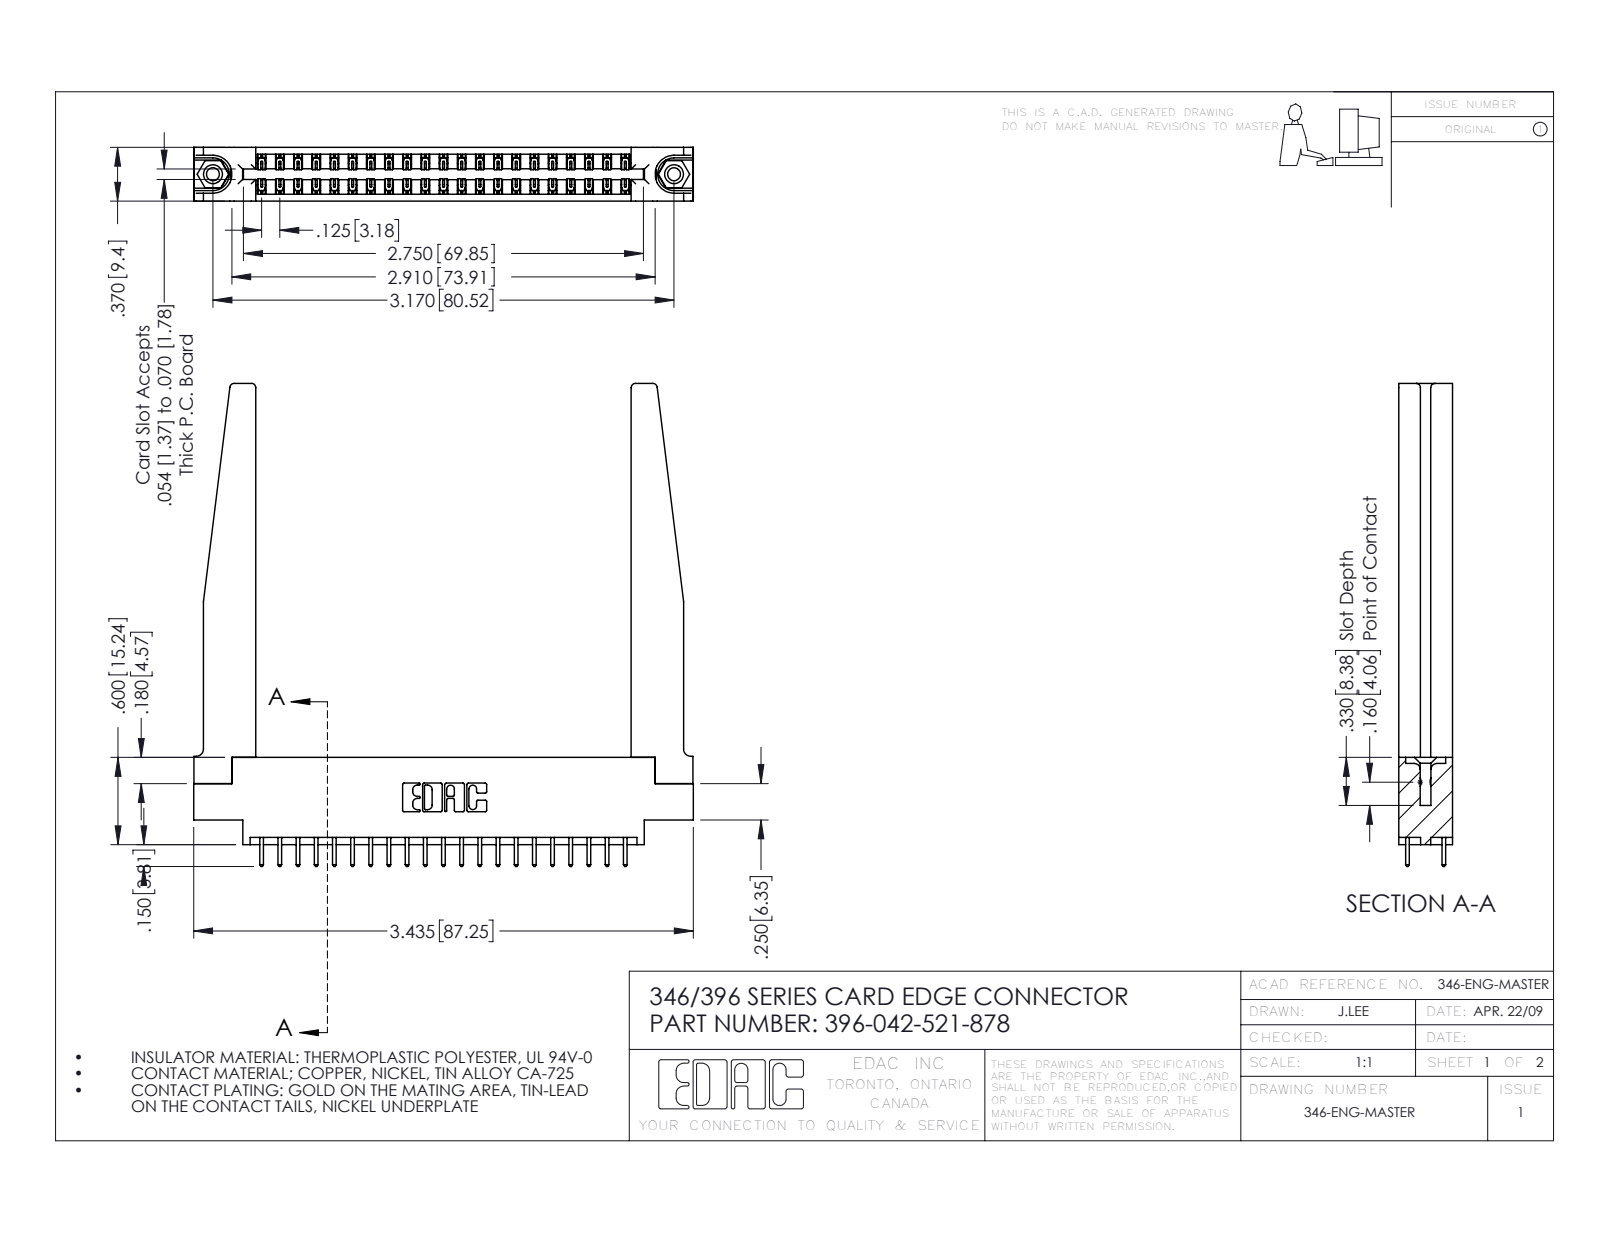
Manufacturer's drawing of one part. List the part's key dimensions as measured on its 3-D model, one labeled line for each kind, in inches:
Part name (STEP PRODUCT): 345-250-001_345-250-001-102; 346 Part_0.170 Offset - 0.156 Dia-TH; 396-042-521-878; 346-220-078_345-220-078 (+1 more)
STEP written by: SolidWorks 2016 (CONFIG_CONTROL_DESIGN)
Units: inches
Bodies: 47 solids, 2544 faces (1692 planar, 800 cylindrical, 52 other)
Overall size (bounding box): 3.435 × 3.32 × 0.37
Volume: 0.92 in³ · Surface area: 27.13 in²
Round holes (diameter × count): ⌀0.089 ×2, ⌀0.125 ×2, ⌀0.156 ×2, ⌀0.064 ×1
Round bosses / shafts (diameter × count): ⌀0.155 ×2
Partial cylindrical surfaces — rounded edges, fillets, slot ends (radius × count): R0.006 ×63, R0.01 ×42, R0.01 ×22, R0.03 ×8, R0.007 ×6, R0.031 ×6, R0.026 ×3, R0.014 ×2
Main face-to-face distances: 0.37, 0.048, 0.322, 0.072, 0.148, 0.15, 0.25, 0.298, 0.025, 0.275
Hole centre spacings: 0.246, 2.963, 3.17
